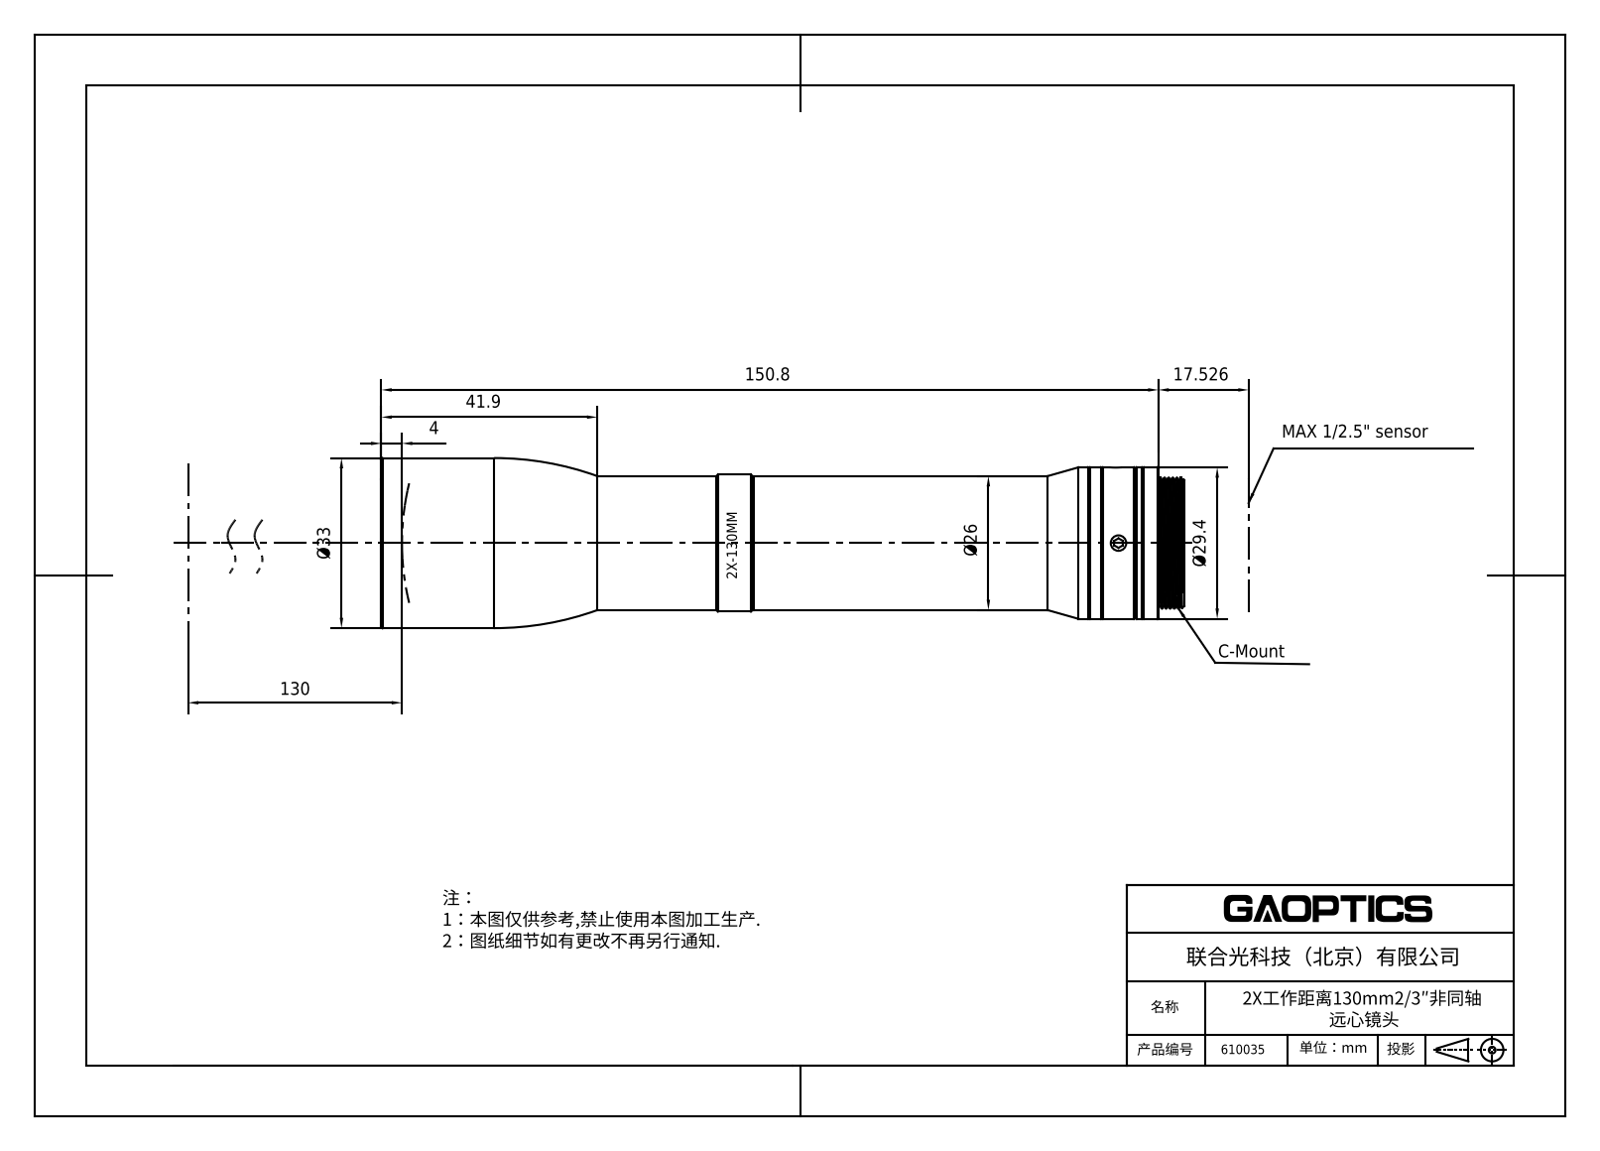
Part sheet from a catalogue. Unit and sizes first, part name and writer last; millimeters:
Units: millimetres
Overall size (bounding box): 161.2 × 33 × 33
Round holes (diameter × count): ⌀2.4 ×3, ⌀27.1 ×1
Round bosses / shafts (diameter × count): ⌀25.4 ×1, ⌀24.34 ×1
Partial cylindrical surfaces — rounded edges, fillets, slot ends (radius × count): R0.8 ×2, R6.15 ×1, R6.95 ×1, R7.25 ×1, R7.35 ×1, R10.5 ×1, R11.05 ×1, R11.5 ×1
Main face-to-face distances: 0.34, 0.5, 152.43, 152.09, 1, 1.5, 147.54, 3.11, 3, 147.2
Volume: 94 757 mm³ · Surface area: 18 834 mm²
Bodies: 4 solids, 356 faces (129 planar, 54 cylindrical, 173 other)
Part name (STEP PRODUCT): 610035
STEP written by: SolidWorks 2020 (CONFIG_CONTROL_DESIGN)
